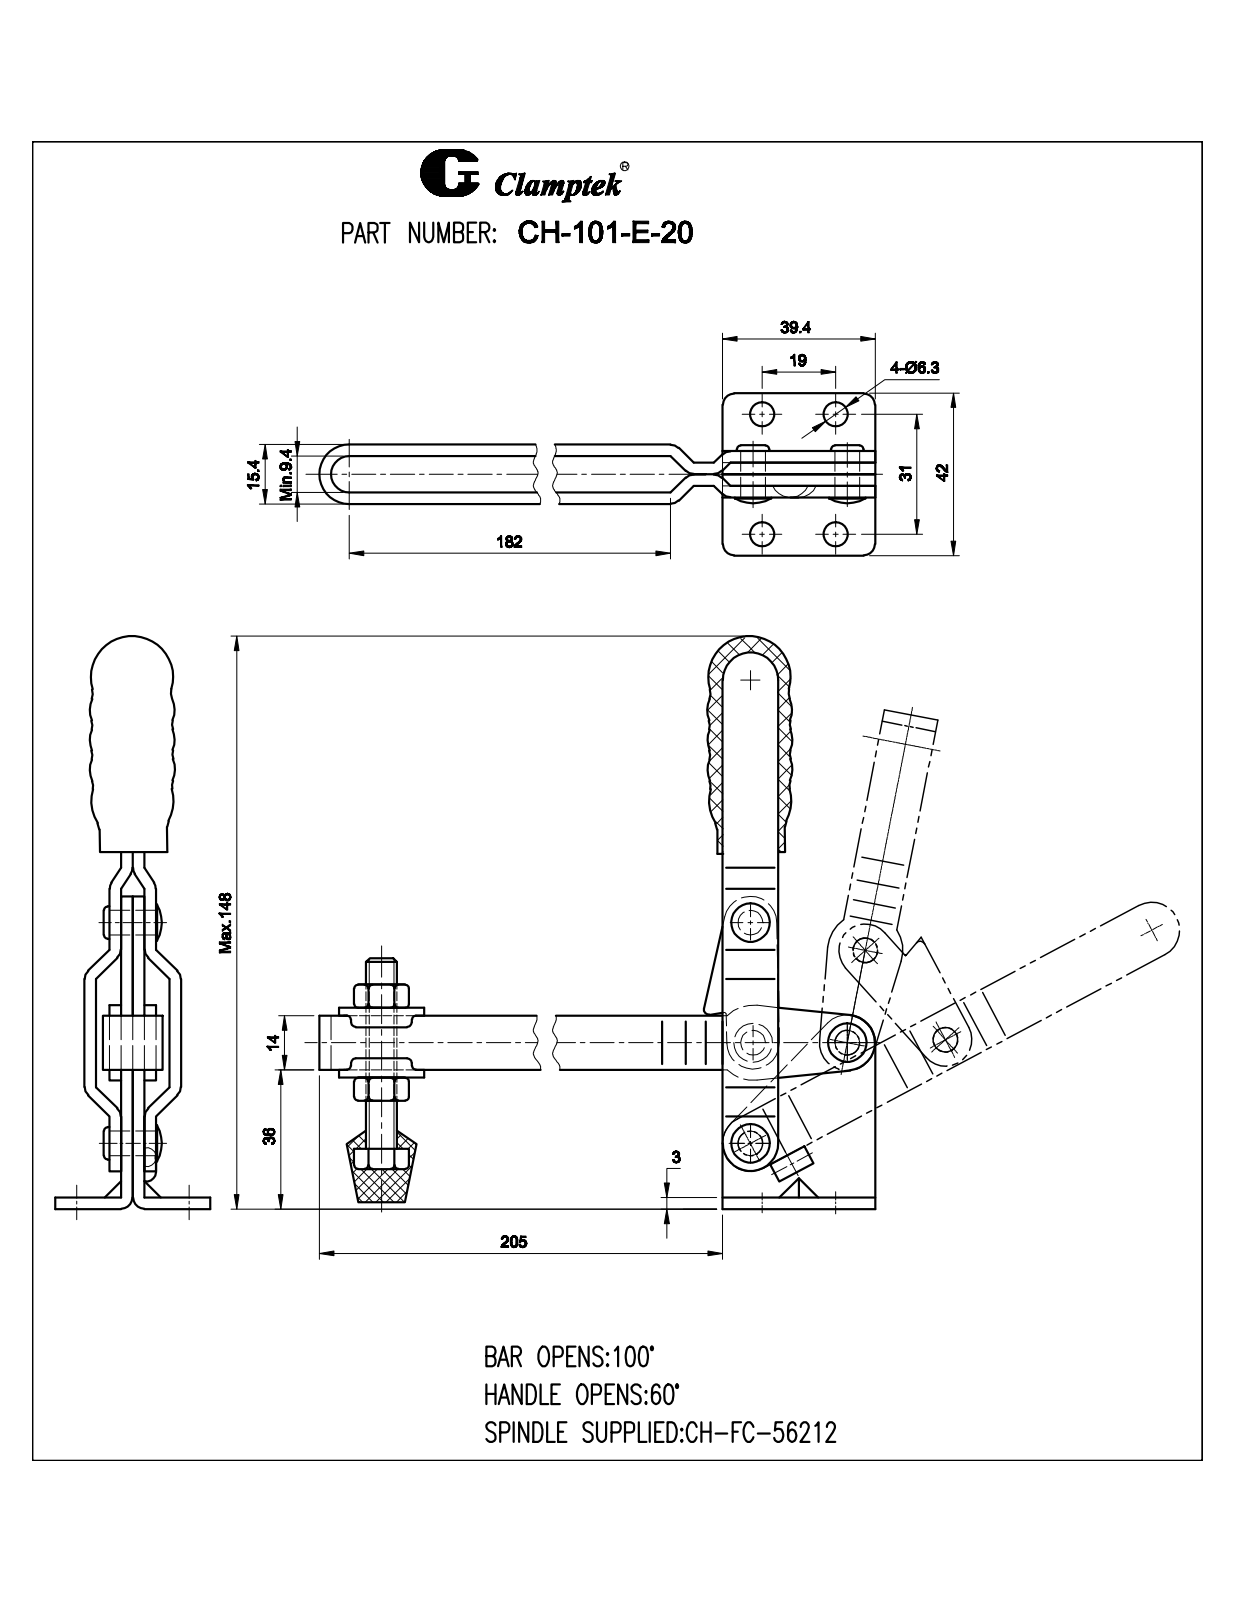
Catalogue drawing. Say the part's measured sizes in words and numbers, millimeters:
The part is named "CH-101-D-06; CH-101-D-04 CONNECTING-PLATE; CH-101-E-20; CH-101-D-01 FLANGED BASE (+6 more)". Its 3-D file was written by "SolidWorks 2010 (CONFIG_CONTROL_DESIGN)". It is 19 solids with 882 faces: 333 planar, 254 cylindrical and 295 other. Overall it measures 245.58 by 151.59 by 42 millimeters. Its volume is 76 666 cubic millimeters and its surface area 59 756 square millimeters. Round holes: 5 of diameter 6.3, 4 of diameter 5.8, 4 of diameter 6.4, 2 of diameter 6.37, 2 of diameter 8.1, 1 of diameter 2.07, 1 of diameter 7.92. Round bosses or shafts: 1 of diameter 20.85, 1 of diameter 7.92, 1 of diameter 1.84. Partial cylindrical surfaces (rounded edges, fillets, slot ends): 16 of radius 3, 10 of radius 1, 8 of radius 3, 4 of radius 2, 4 of radius 3, 3 of radius 7.2, 2 of radius 4.7, 2 of radius 6.8. The main face-to-face distances are 3, 6, 7.71, 4.7, 4.71, 7.7, 12.41, 1.7, 10.71, 1.71. The hole center spacings are 19, 31, 36.36, 24.3, 26.08, 31.01, 36.07, 41.
